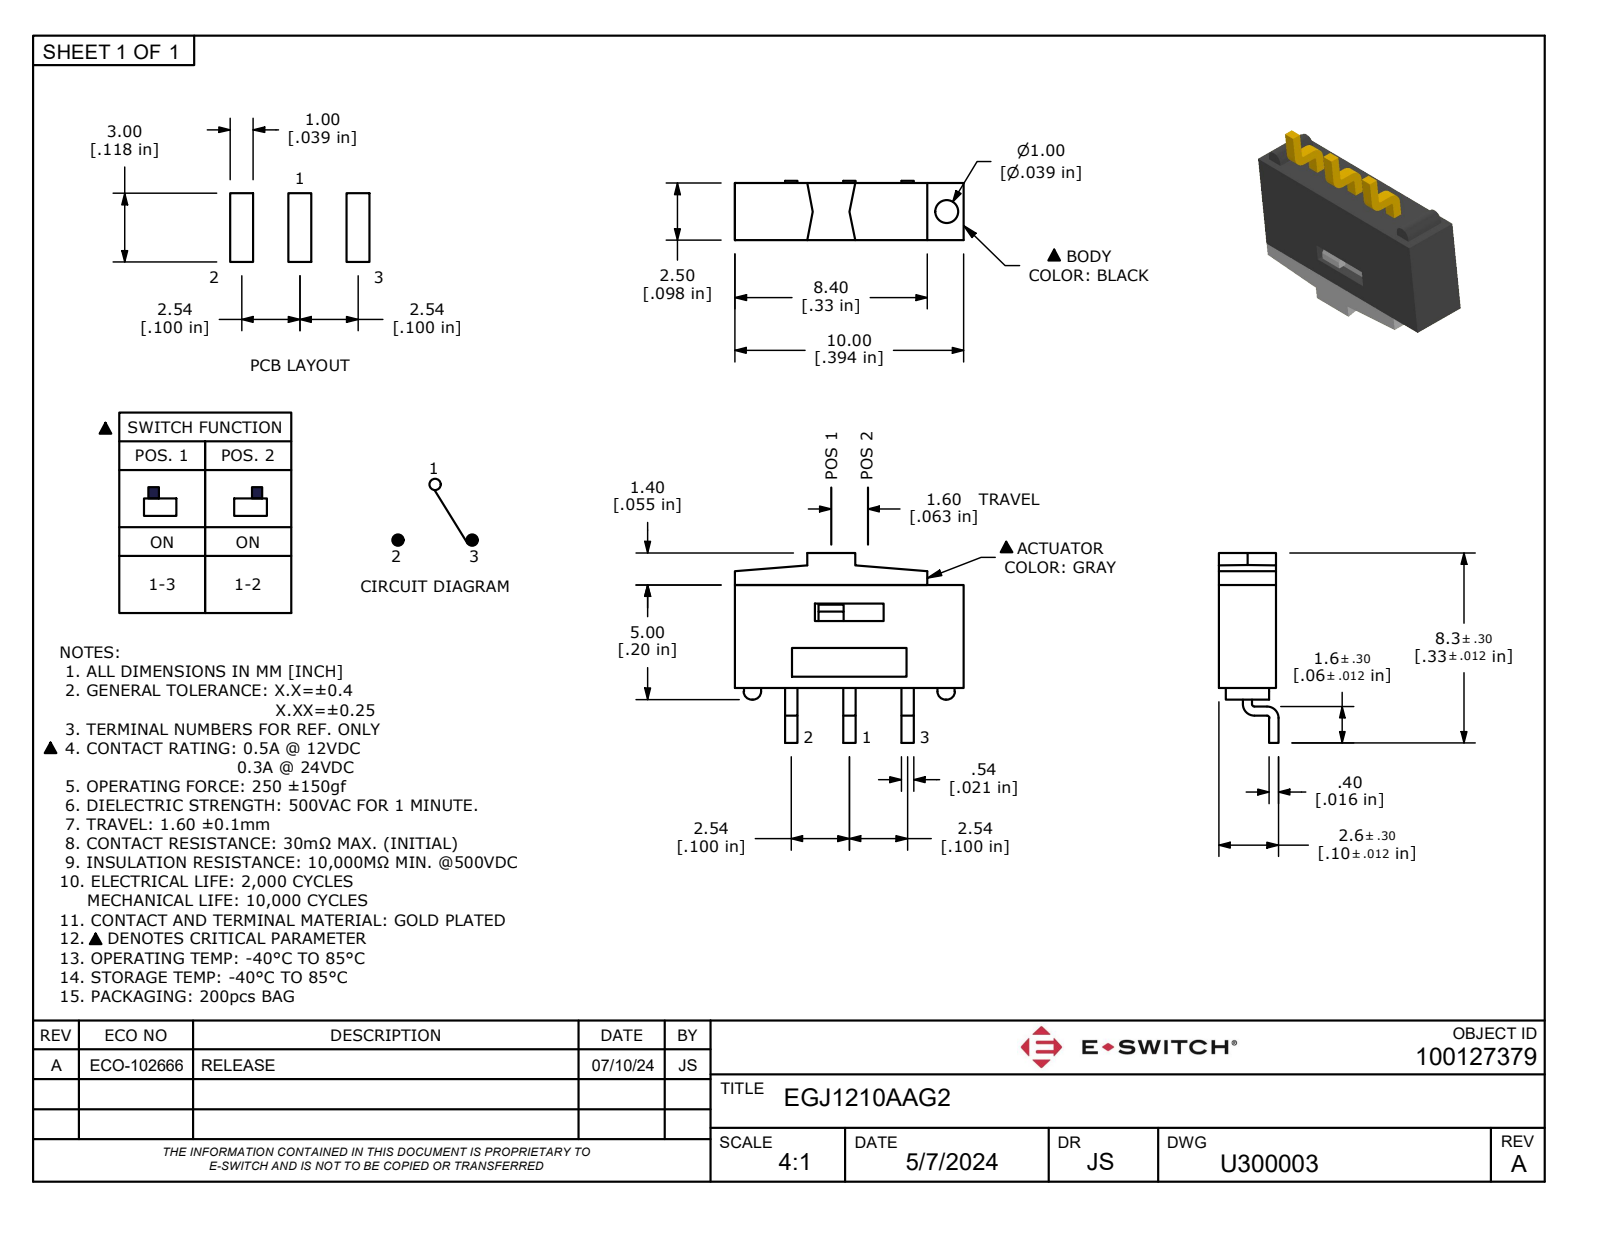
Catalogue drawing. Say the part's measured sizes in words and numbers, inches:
The part is named "EGJ1210AAG2". Its 3-D file was written by "Autodesk Inventor 2022 (AUTOMOTIVE_DESIGN)". It is 1 solid with 107 faces: 90 planar, 17 cylindrical and 0 other. Overall it measures 0.394 by 0.327 by 0.102 inches. Its volume is 0.006 cubic inches and its surface area 0.509 square inches. Round holes: 1 of diameter 0.039. Partial cylindrical surfaces (rounded edges, fillets, slot ends): 4 of radius 0.014, 2 of radius 0.004, 2 of radius 0.02. The main face-to-face distances are 0.017, 0.081, 0.098, 0.02, 0.065, 0.062, 0.079, 0.067, 0.327, 0.394.
